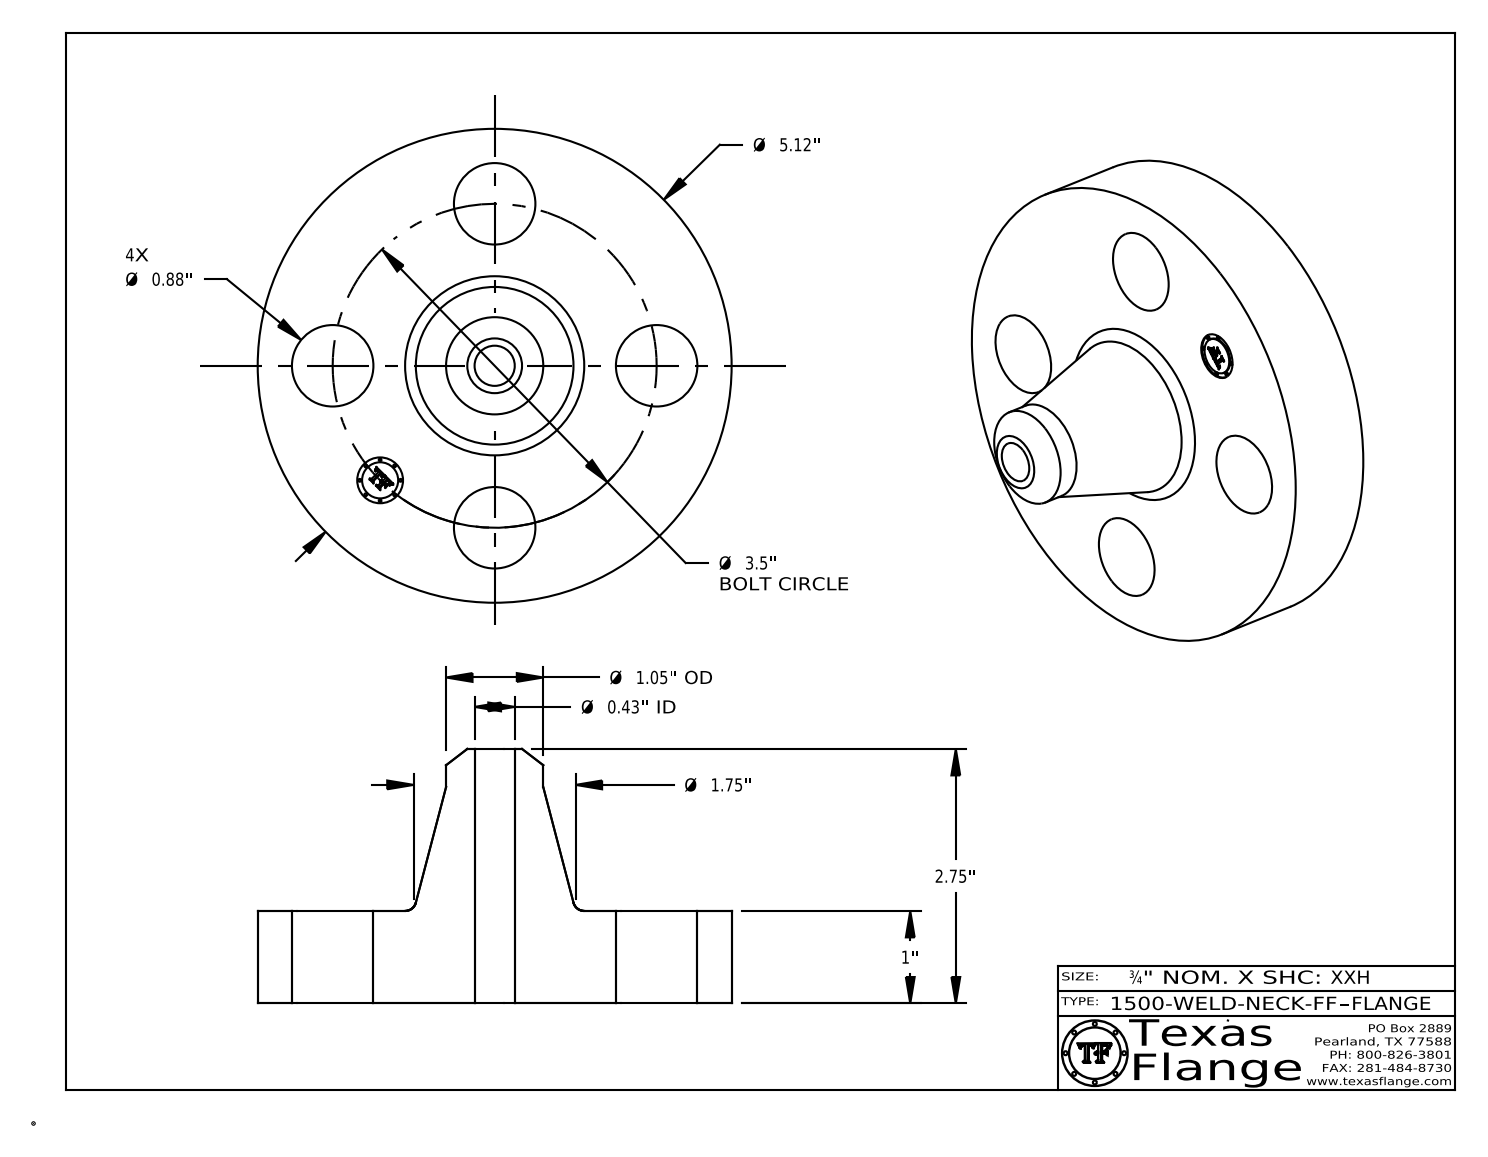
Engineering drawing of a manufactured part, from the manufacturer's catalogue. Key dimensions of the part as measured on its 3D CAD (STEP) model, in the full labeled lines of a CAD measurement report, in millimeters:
Part name (STEP PRODUCT): 1500-WELD-NECK-FF
STEP written by: CATIA V5 STEP AP214 (AUTOMOTIVE_DESIGN)
Units: millimetres
Bodies: 1 solid, 408 faces (368 planar, 34 cylindrical, 6 other)
Overall size (bounding box): 130 × 130 × 69.9
Volume: 330 400 mm³ · Surface area: 46 660 mm²
Round holes (diameter × count): ⌀22.4 ×4, ⌀11 ×1, ⌀12.6 ×1
Round bosses / shafts (diameter × count): ⌀0.8 ×8, ⌀130 ×1, ⌀26.7 ×1, ⌀9.9 ×1
Main face-to-face distances: 25.4, 69.9, 44.5, 0.4, 25, 44.8, 3.8, 3.7, 0.7, 2.4
Hole centre spacings: 44.5, 62.9, 34, 82.1, 88.9
